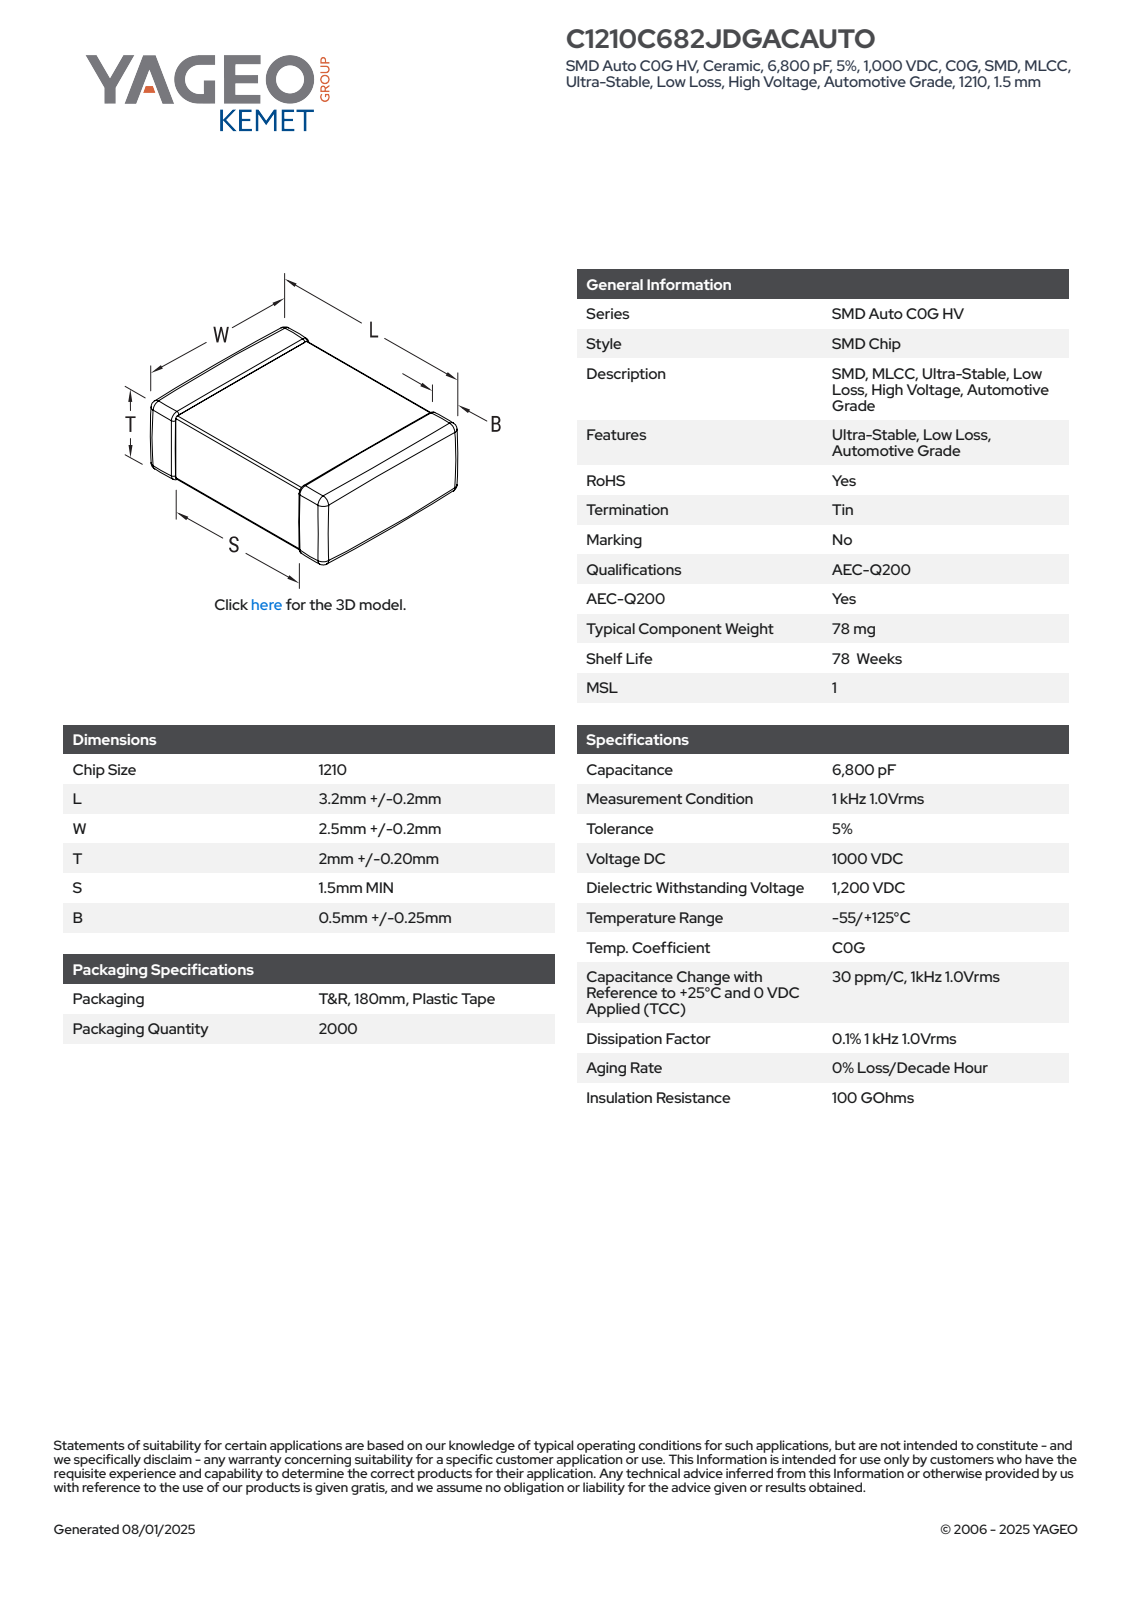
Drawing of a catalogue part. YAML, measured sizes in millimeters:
part_name: "CCS_CCSTD_1210_L3.4W2.7T2.2B0.5"
step_written_by: "SolidWorks 2021 (AUTOMOTIVE_DESIGN)"
units: millimeters
bodies: {solids: 4, faces: 125, planar: 71, cylindrical: 38, other: 16}
overall_size: [3.4, 2.7, 2.2]
volume: 19
surface_area: 45
face_to_face_distances: [2.14, 3.4, 2.64, 2.08, 2.58, 2.2, 2.7, 2.15, 2.09, 0.4]
